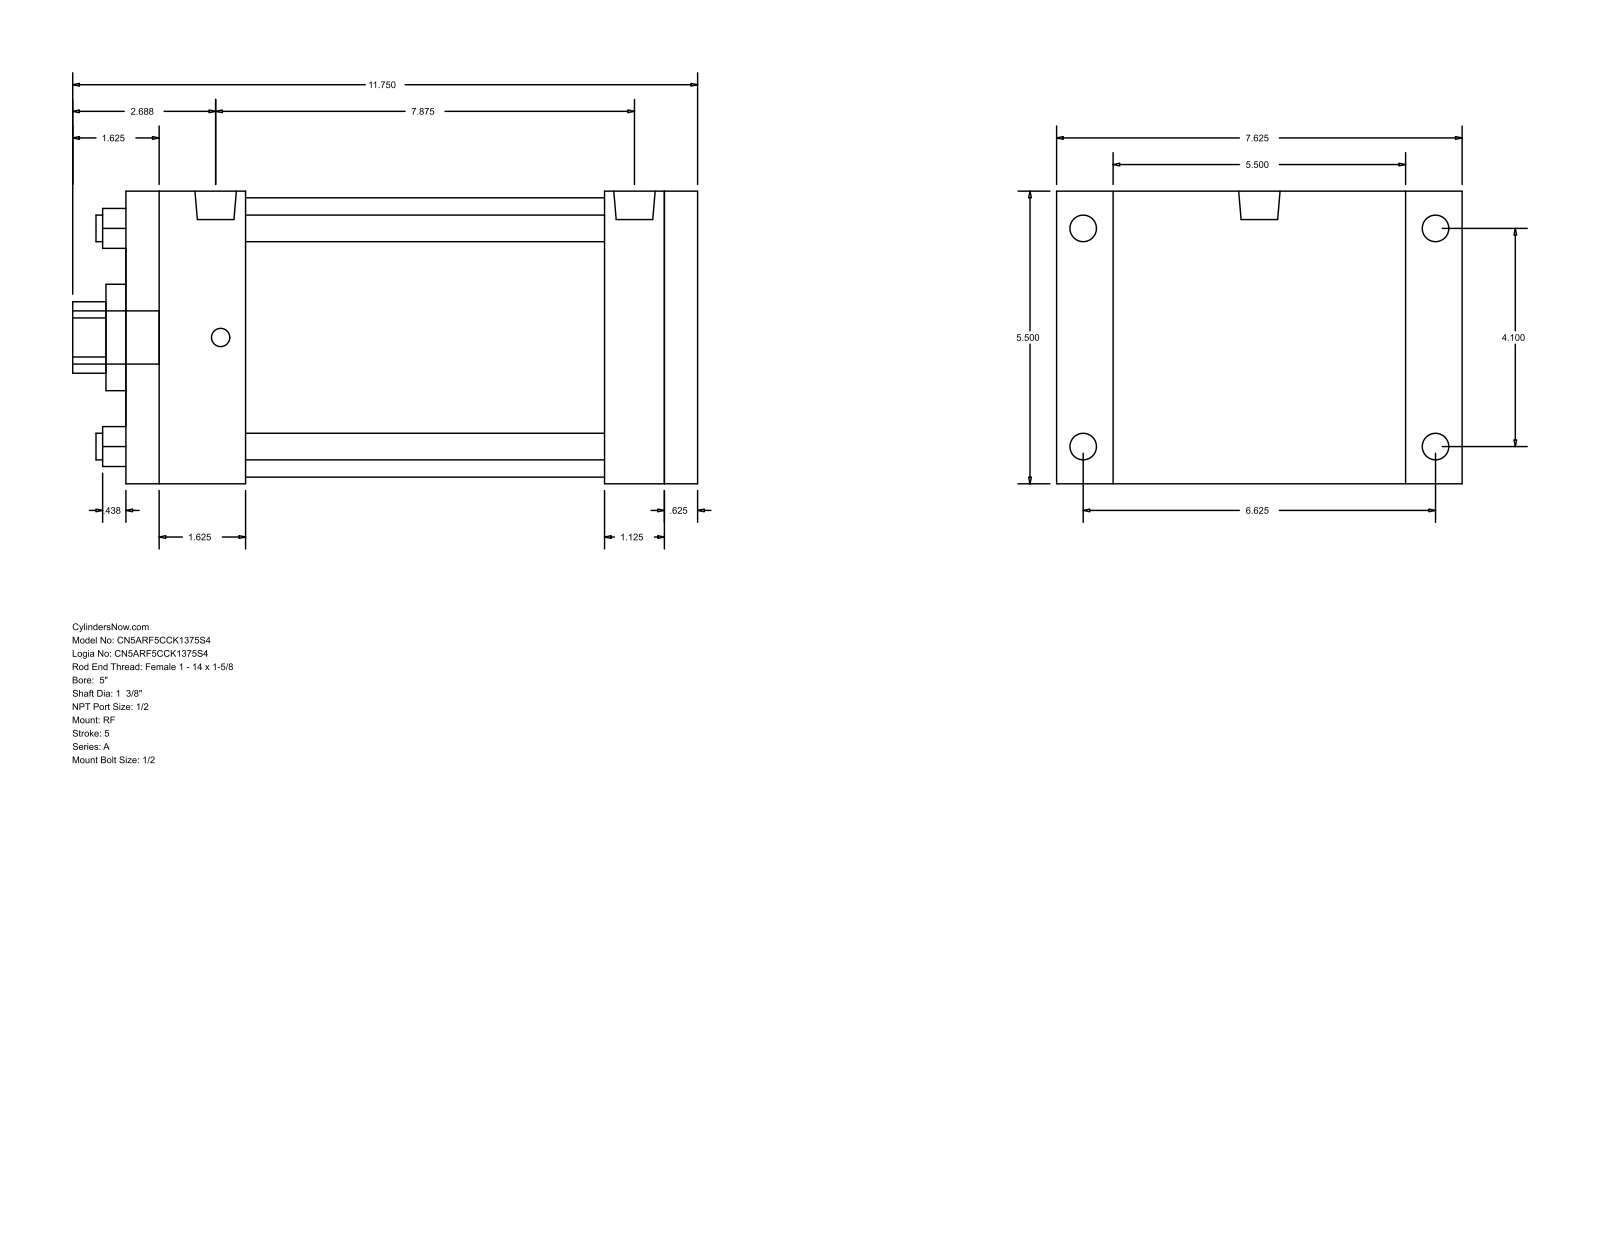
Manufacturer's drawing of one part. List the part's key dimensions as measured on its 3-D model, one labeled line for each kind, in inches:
Part name (STEP PRODUCT): A_RF__0500_1.375
STEP written by: GSSL Pune (CONFIG_CONTROL_DESIGN)
Units: inches
Bodies: 0 solids, 92 faces (64 planar, 28 cylindrical, 0 other)
Overall size (bounding box): 11.75 × 7.625 × 5.5
Round holes (diameter × count): ⌀0.5 ×4, ⌀1.375 ×1, ⌀2 ×1, ⌀5.25 ×1
Round bosses / shafts (diameter × count): ⌀0.5 ×4, ⌀0.344 ×4, ⌀0.778 ×2, ⌀1 ×1
Partial cylindrical surfaces — rounded edges, fillets, slot ends (radius × count): R0.672 ×1
Main face-to-face distances: 5.5, 10.75, 0.625, 10.125, 1.125, 2.25, 7.875, 8.5, 9, 6.75
Hole centre spacings: 2.899, 4.1, 5.798
